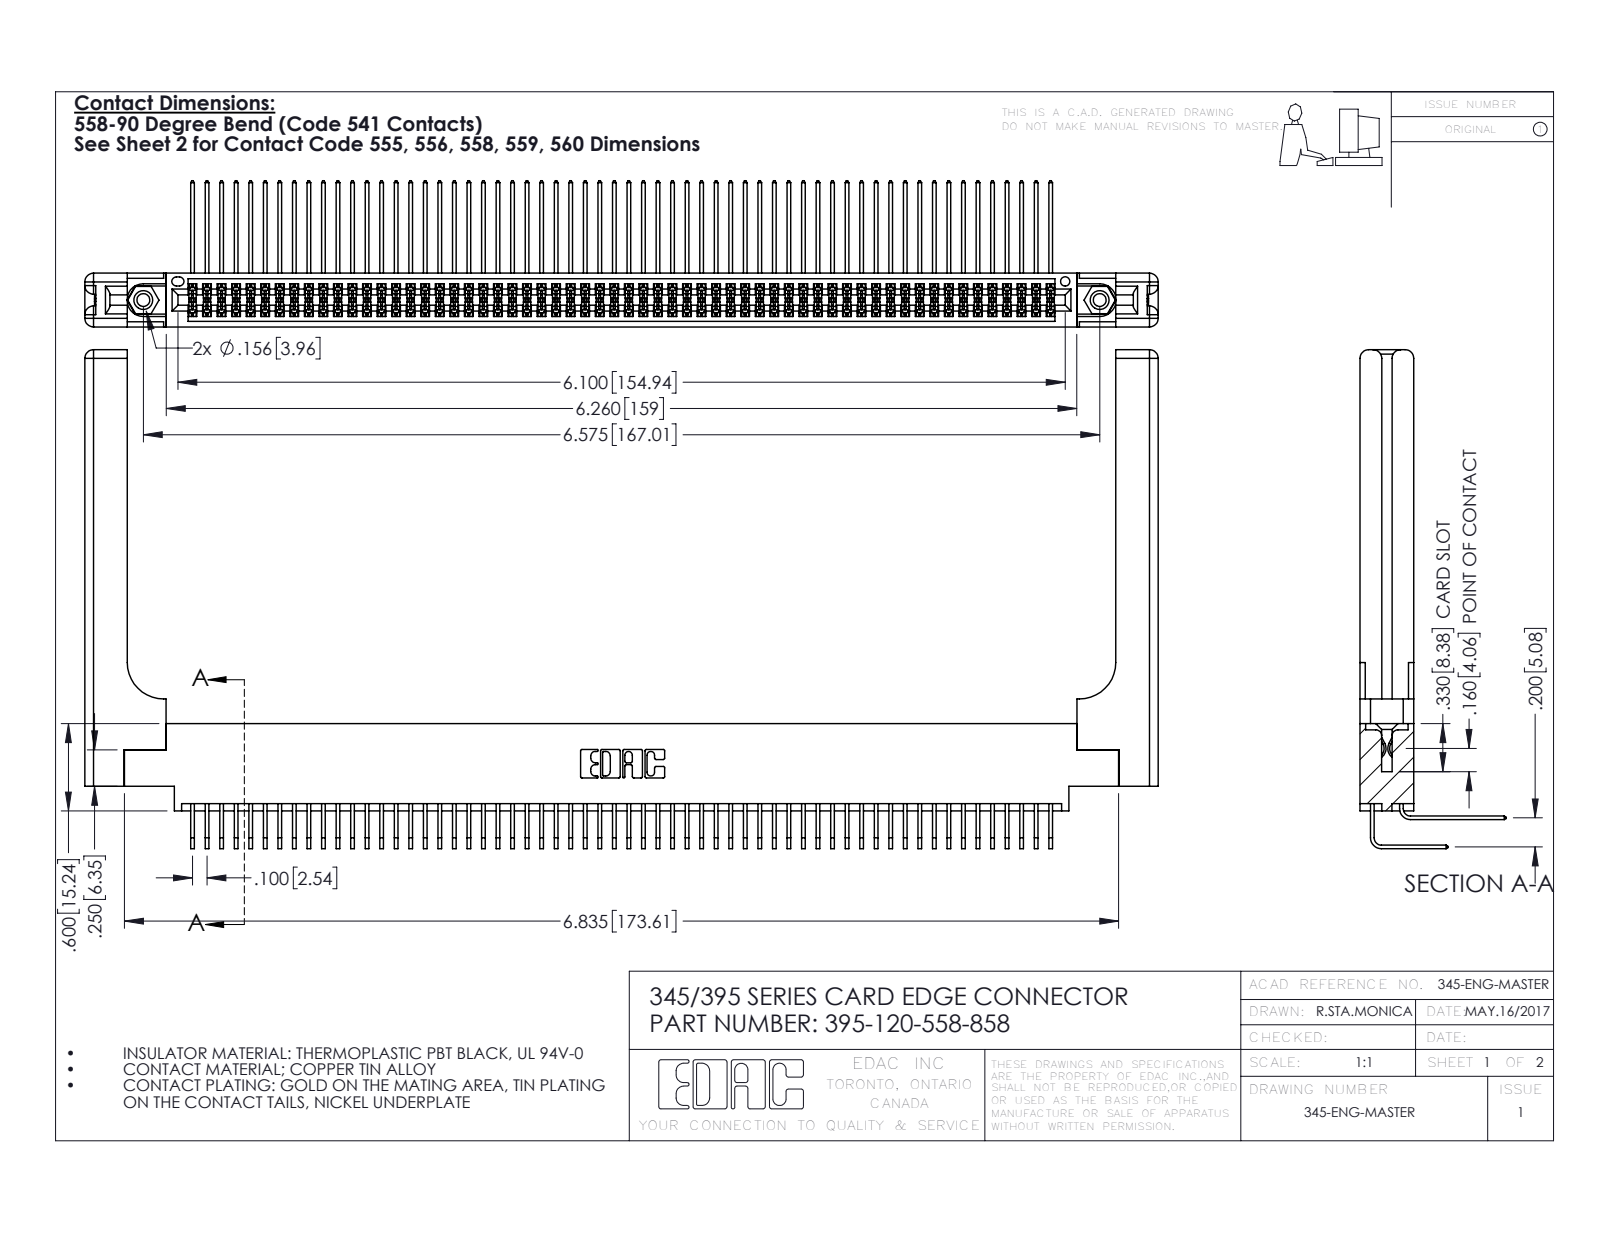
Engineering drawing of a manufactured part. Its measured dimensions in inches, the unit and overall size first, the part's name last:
Units: inches
Overall size (bounding box): 7.379 × 3.429 × 1.005
Round holes (diameter × count): ⌀0.089 ×2, ⌀0.125 ×2, ⌀0.156 ×2, ⌀0.064 ×1
Round bosses / shafts (diameter × count): ⌀0.155 ×2
Partial cylindrical surfaces — rounded edges, fillets, slot ends (radius × count): R0.006 ×181, R0.01 ×22, R0.06 ×16, R0.007 ×6, R0.031 ×6, R0.026 ×3, R0.014 ×2, R0.019 ×2
Main face-to-face distances: 0.072, 0.298, 0.37, 0.2, 0.098, 0.272, 0.025, 0.225, 0.175, 0.148
Hole centre spacings: 0.27, 6.339, 6.575
Volume: 1.674 in³ · Surface area: 57.07 in²
Bodies: 125 solids, 6626 faces (4432 planar, 2134 cylindrical, 60 other)
Part name (STEP PRODUCT): 345 Part_0.170 Offset - 0.156 Dia-TH; 345-292-001_558 559 Tail - 1; 345-250-001_345-250-001-102; 345-292-001_558 Tail - 2 (+2 more)
STEP written by: SolidWorks 2016 (CONFIG_CONTROL_DESIGN)
